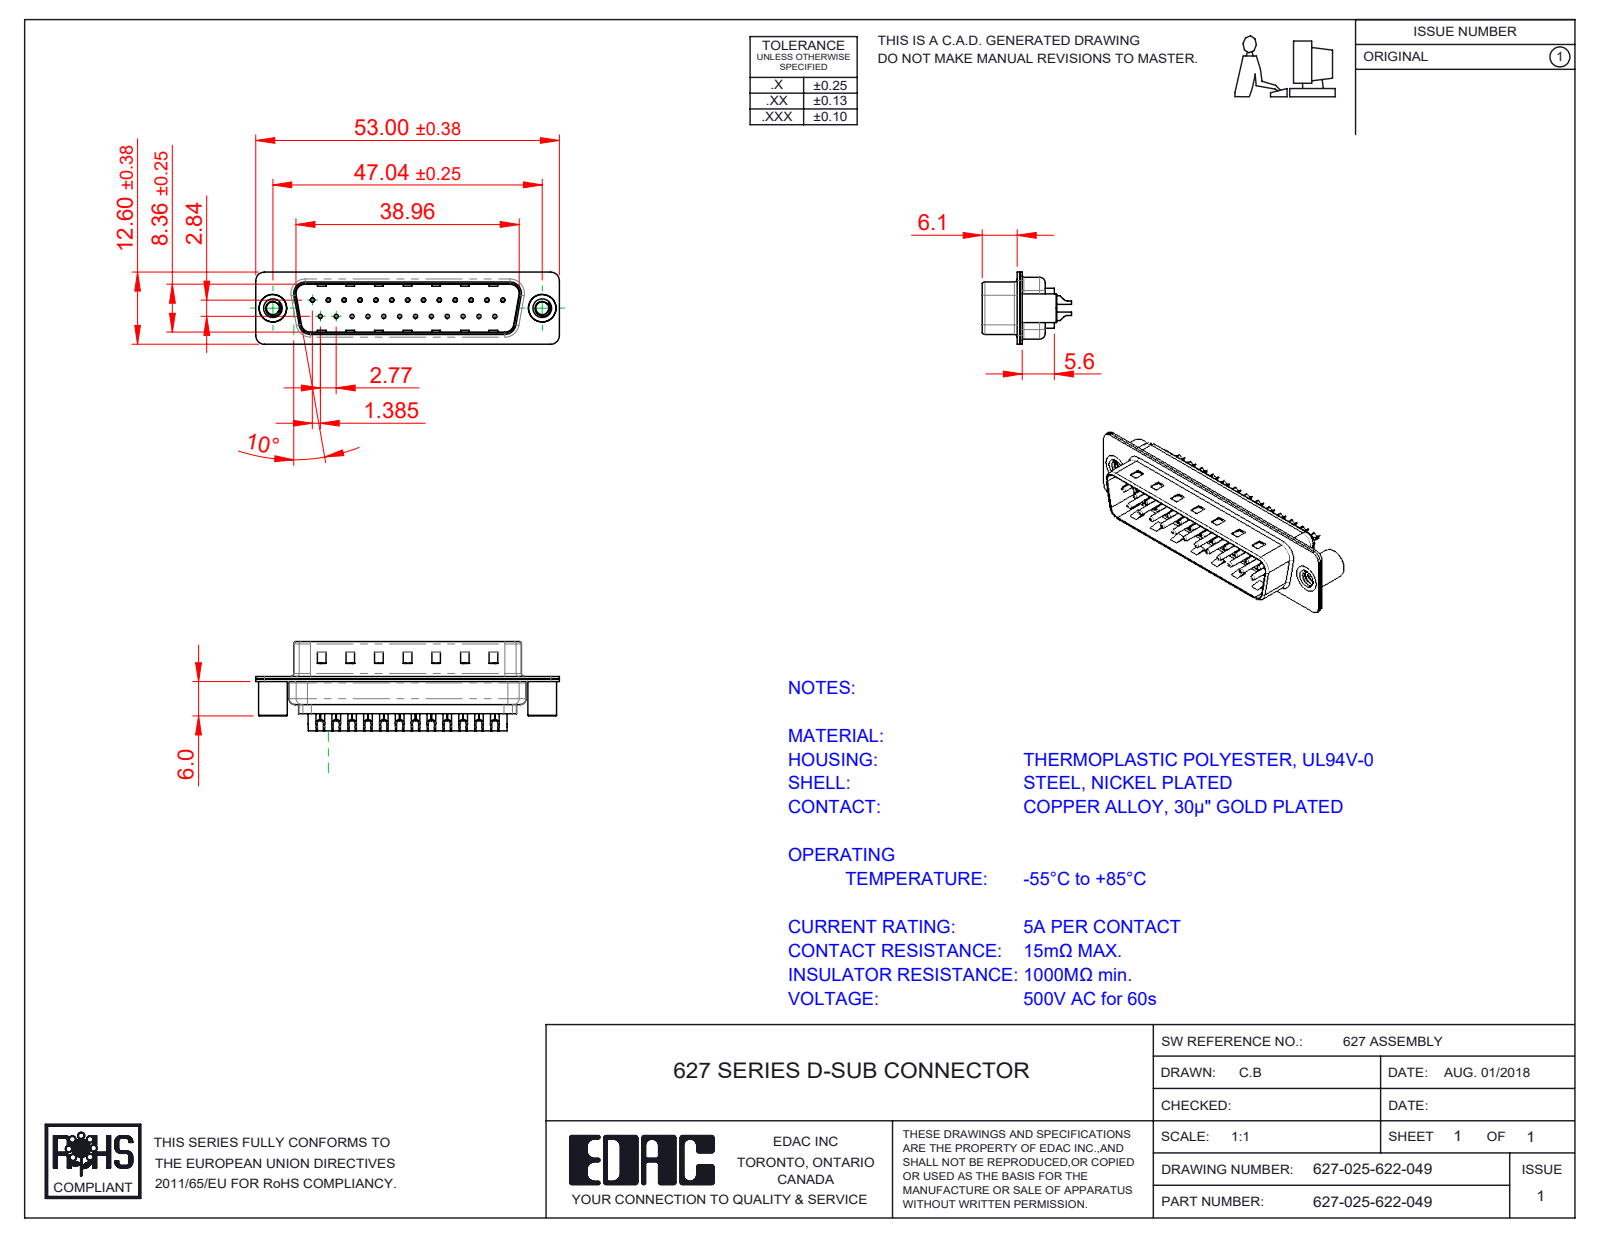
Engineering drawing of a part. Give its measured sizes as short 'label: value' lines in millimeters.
name: 627 4-40 Threaded Standoff BS; 627 Contact Row 1_22L; 627-025-622-049; 627 Contact Row 2_22L (+3 more)
written by: SolidWorks 2020 (CONFIG_CONTROL_DESIGN)
unit: mm
bodies: 30 solids, 1998 faces (521 planar, 882 cylindrical, 595 other)
size: 53 × 15.35 × 12.6
volume: 2 787 mm³; area: 8 046 mm²
holes: 25× ⌀0.35, 25× ⌀1.1, 25× ⌀1.6, 2× ⌀2.26, 2× ⌀4, 2× ⌀4.8
bosses: 25× ⌀2, 25× ⌀1.5, 25× ⌀0.75, 2× ⌀5, 2× ⌀4.9
rounds: 16× R1.5, 12× R2, 8× R0.5, 8× R1.6, 6× R1, 4× R0.25, 4× R0.6, 4× R0.65
face distances: 0.4, 0.45, 0.82, 9.58, 8.76, 0.9, 1.5, 6.5, 1.4, 6.05
hole spacings: 3.16, 8.31, 2.77, 5.54, 11.08, 16.62, 5.03, 5.04
